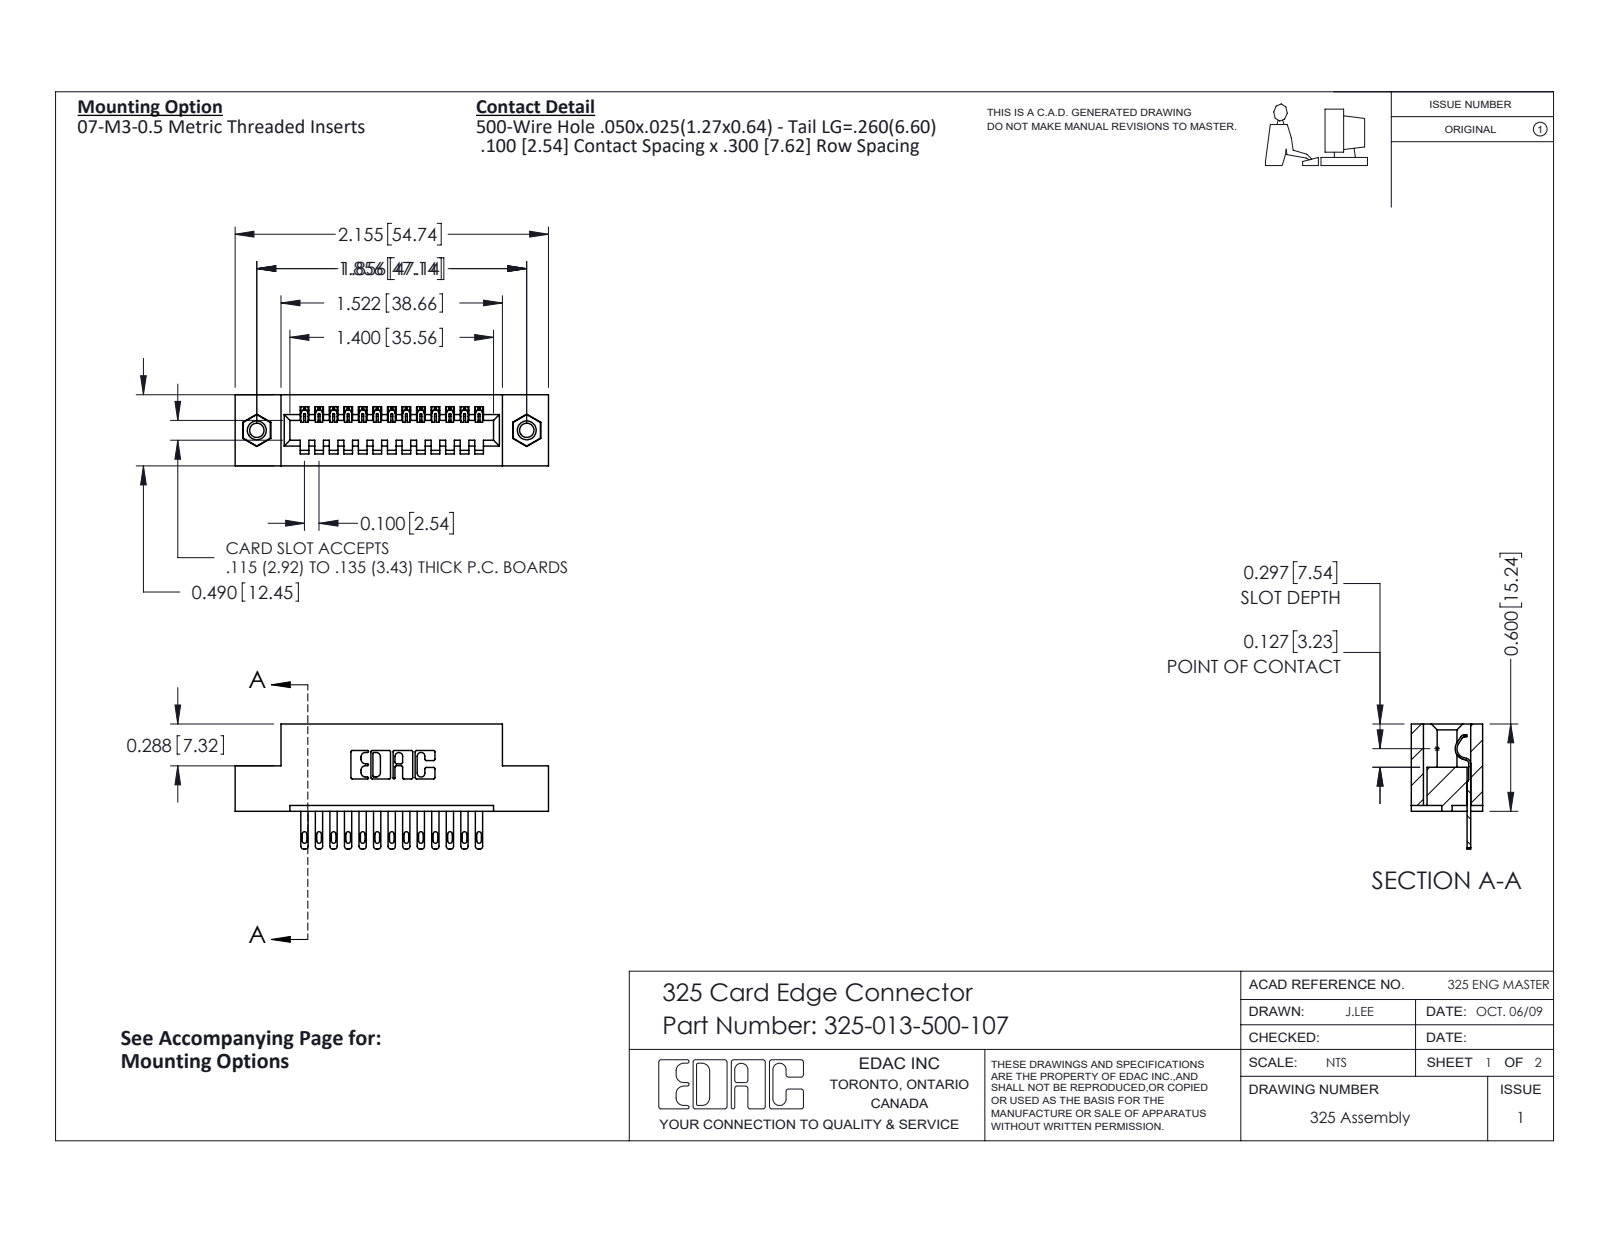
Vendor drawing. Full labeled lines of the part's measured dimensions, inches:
Part name (STEP PRODUCT): 325-292-001_325-293-100; 325 Part_TI; 325-013-500-107; 345-250-001_345-250-005-103
STEP written by: SolidWorks 2016 (CONFIG_CONTROL_DESIGN)
Units: inches
Bodies: 16 solids, 876 faces (570 planar, 290 cylindrical, 16 other)
Overall size (bounding box): 2.155 × 0.86 × 0.49
Volume: 0.41 in³ · Surface area: 10.7 in²
Round holes (diameter × count): ⌀0.098 ×2, ⌀0.125 ×2, ⌀0.16 ×2
Round bosses / shafts (diameter × count): ⌀0.155 ×2
Partial cylindrical surfaces — rounded edges, fillets, slot ends (radius × count): R0.006 ×26, R0.016 ×26, R0.02 ×26, R0.01 ×22, R0.007 ×6, R0.031 ×6, R0.026 ×3, R0.014 ×1
Main face-to-face distances: 0.083, 0.407, 0.3, 0.49, 0.04, 0.1, 0.107, 0.383, 0.025, 0.6
Hole centre spacings: 1.856
